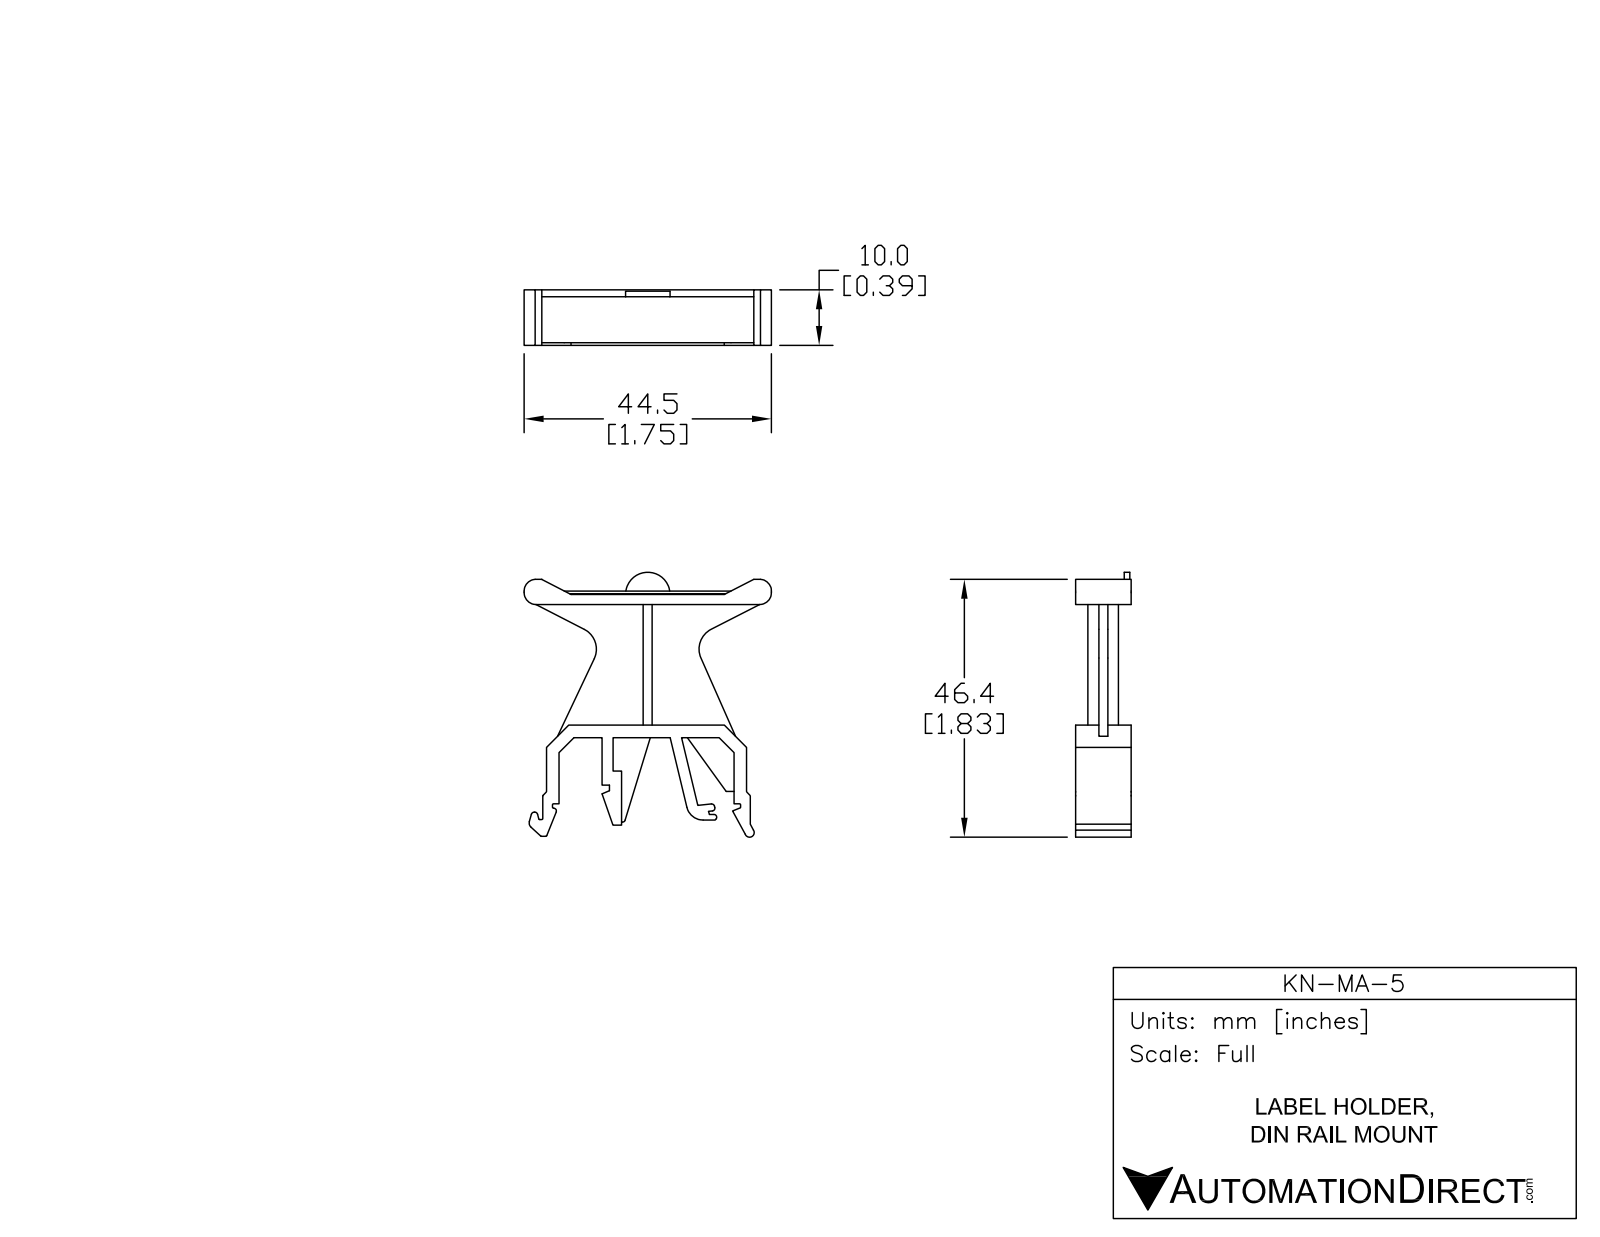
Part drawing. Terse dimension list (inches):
name: KN-MA-5
written by: SolidWorks 2014 (AUTOMOTIVE_DESIGN)
unit: in
bodies: 4 solids, 140 faces (107 planar, 33 cylindrical, 0 other)
size: 1.876 × 1.752 × 0.394
volume: 0.291 in³; area: 11.07 in²
rounds: 12× R0.008, 7× R0.02, 4× R0.083, 3× R0.157, 2× R0.013, 1× R0.033, 1× R0.039, 1× R0.118
face distances: 0.063, 0.165, 0.228, 0.394, 0.02, 0.076, 0.024, 0.071, 0.095, 0.854
